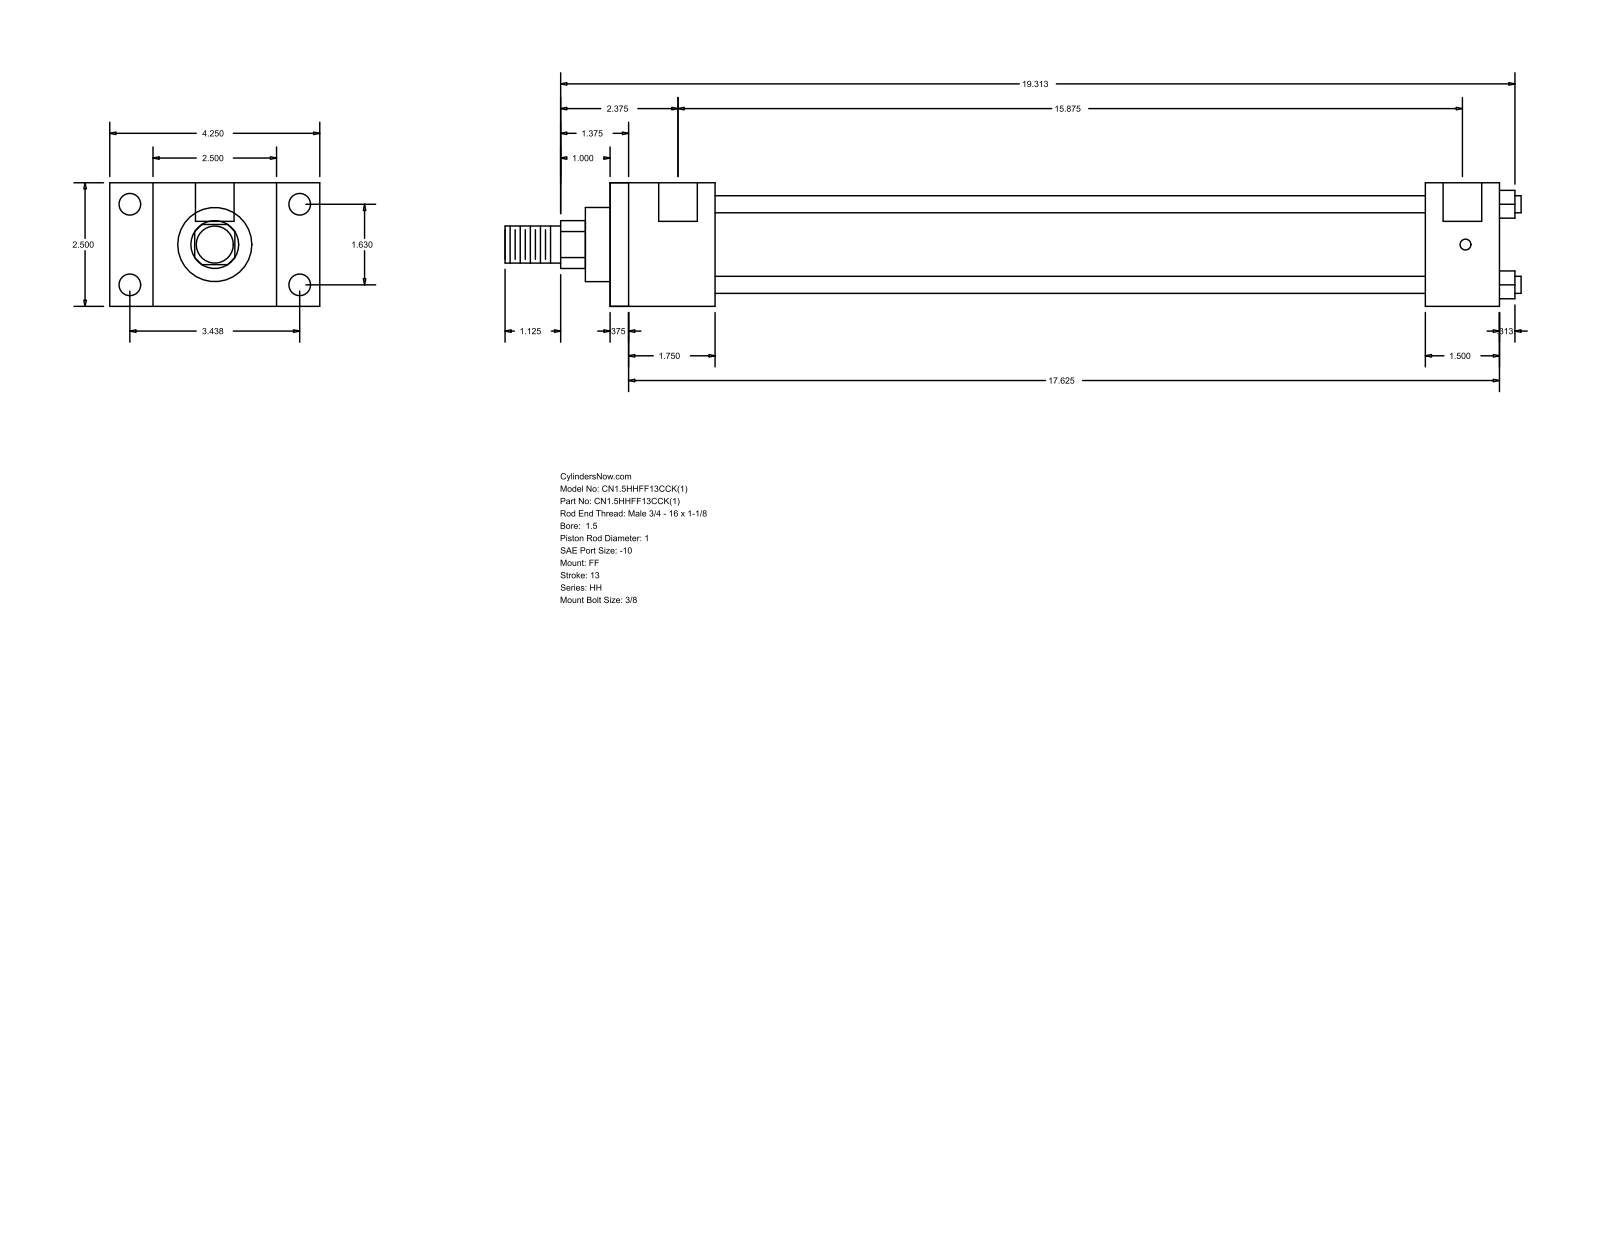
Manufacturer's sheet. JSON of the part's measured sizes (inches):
{"part_name": "HH_FF__0150_1", "step_written_by": "GSSL Pune (CONFIG_CONTROL_DESIGN)", "units": "inches", "bodies": {"solids": 0, "faces": 92, "planar": 64, "cylindrical": 28, "other": 0}, "overall_size": [20.563, 4.25, 2.5], "round_holes": [[0.219, 4], [0.438, 4], [0.781, 2]], "round_bosses_or_shafts": [[0.345, 4], [1.75, 1], [1.5, 1], [1, 1], [0.75, 1]], "partial_cylinders_radius": [[0.484, 1]], "face_to_face_distances": [2.5, 18, 0.375, 17.625, 1.5, 2.125, 1.75, 15.875, 16.5, 16.125], "hole_center_spacings": [0.063, 1.63, 3.438, 3.805, 15.937, 16, 15.875]}
